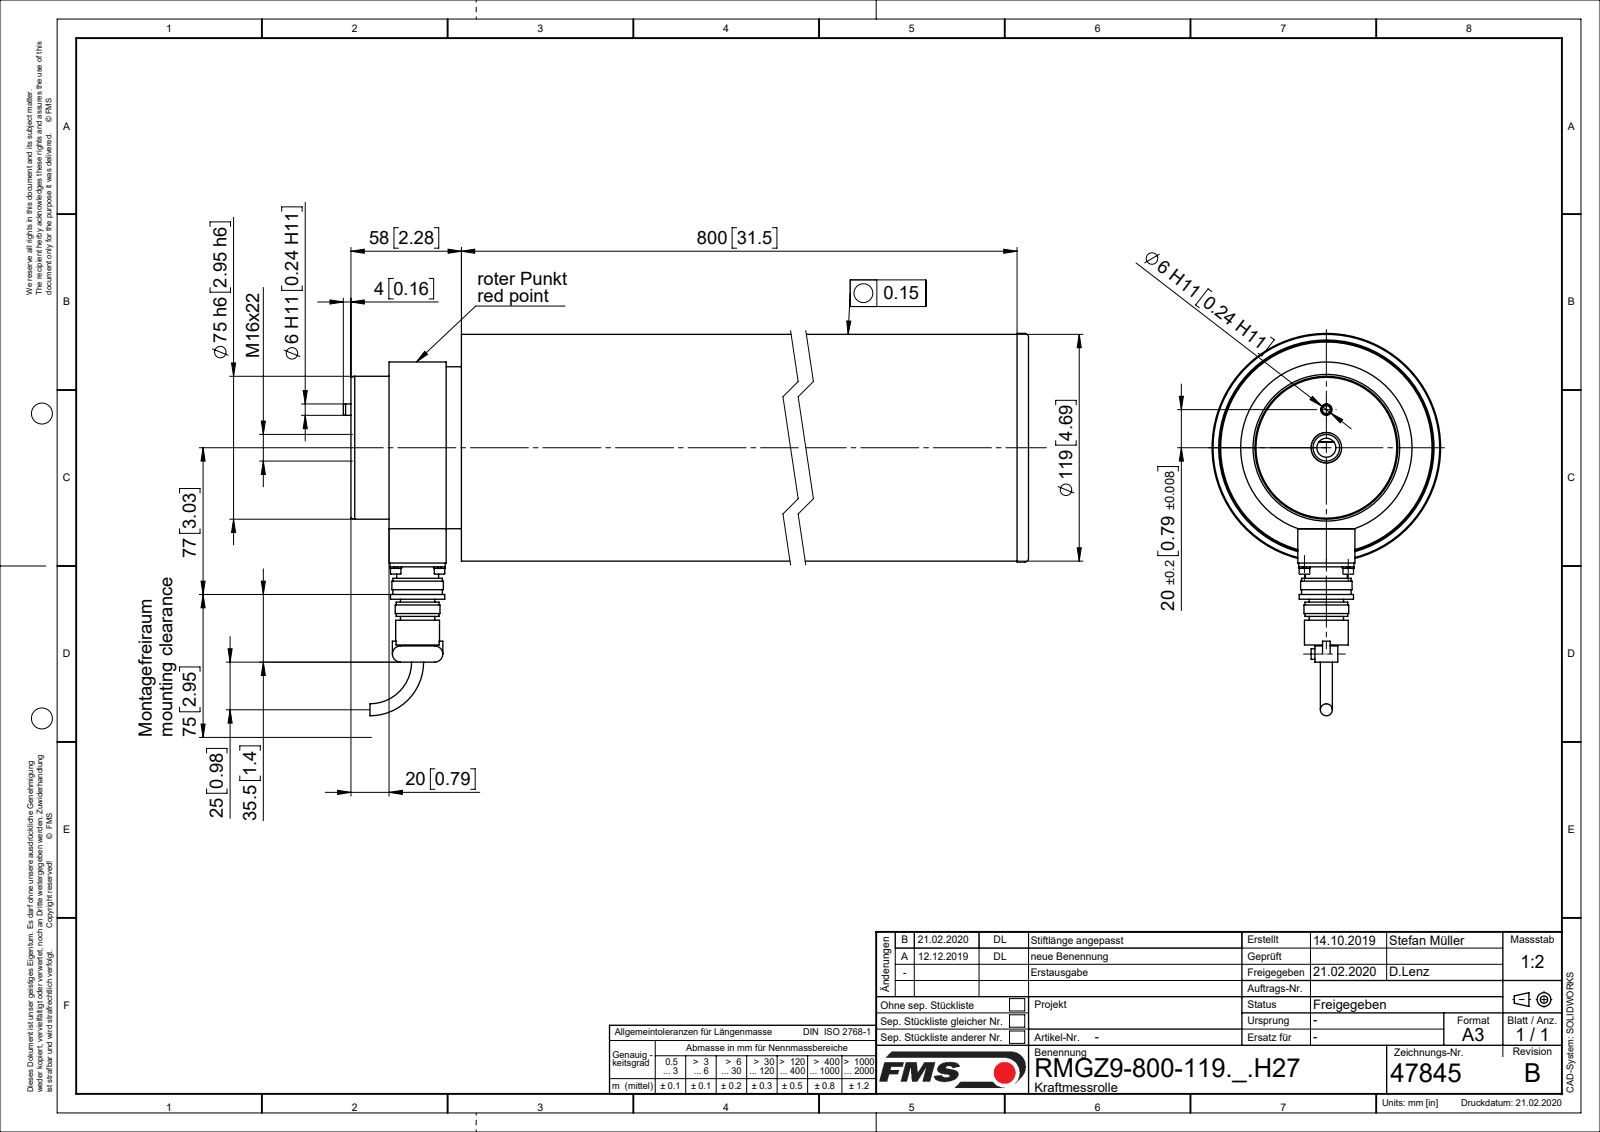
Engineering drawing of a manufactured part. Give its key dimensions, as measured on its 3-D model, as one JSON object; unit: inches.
{"part_name": "130507.4_01; 130507.1_01; 47848_H15; Federringe_DIN127A_M03 (+8 more)", "step_written_by": "SolidWorks 2018 (CONFIG_CONTROL_DESIGN)", "units": "inches", "bodies": {"solids": 31, "faces": 570, "planar": 162, "cylindrical": 234, "other": 174}, "overall_size": [34.173, 7.9, 4.724], "volume_in3": 204.9, "surface_area_in2": 1376, "round_holes": [[0.098, 4], [0.122, 4], [0.134, 4], [0.13, 1], [0.197, 1], [0.236, 1], [0.394, 1], [0.472, 1], [0.551, 1], [0.866, 1], [0.906, 1], [1.024, 1]], "round_bosses_or_shafts": [[0.217, 6], [0.244, 4], [0.118, 4], [0.098, 4], [4.724, 1], [4.685, 1], [4.37, 1], [4.173, 1]], "partial_cylinders_radius": [[0.433, 4], [0.167, 2], [0.689, 1]], "face_to_face_distances": [1.26, 9.488, 1.969, 0.079, 8.937, 18.346, 9.961, 23.819, 10.748, 19.606], "hole_center_spacings": [0.64, 0.906, 1.281, 0.787]}
